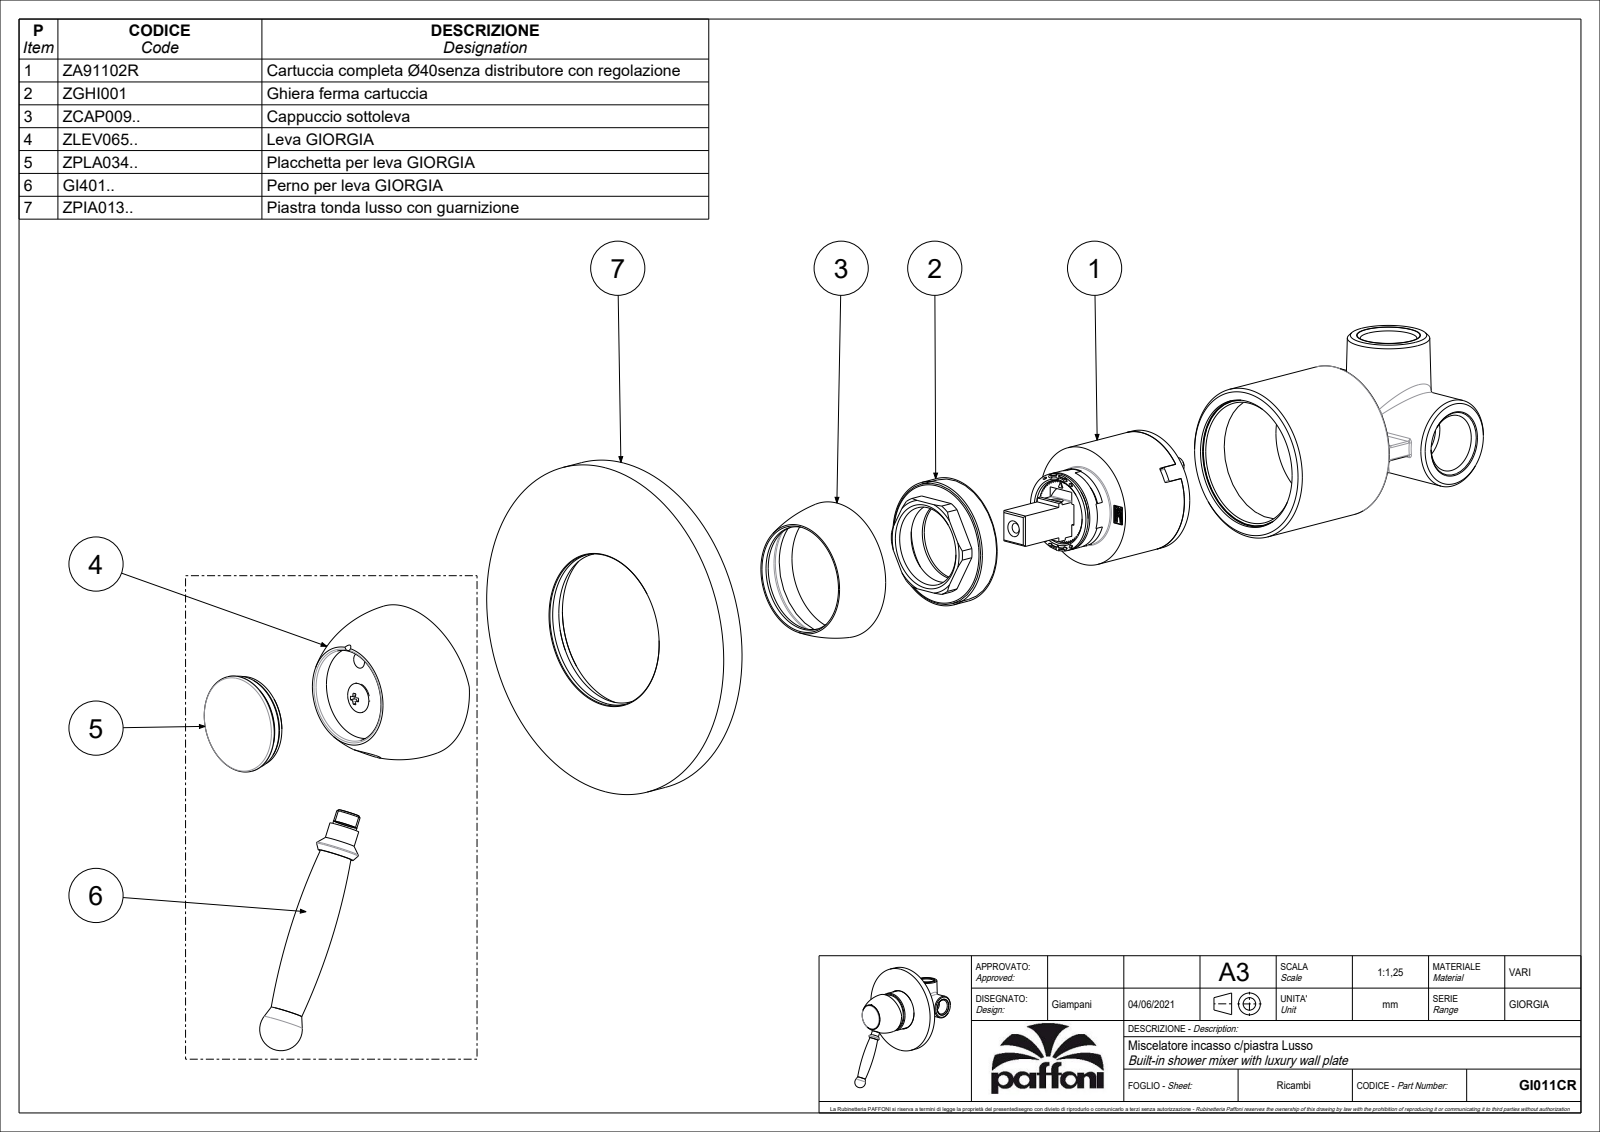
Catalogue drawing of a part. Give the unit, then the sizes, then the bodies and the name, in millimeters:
Units: millimetres
Overall size (bounding box): 146.52 × 110 × 90.37
Round holes (diameter × count): ⌀5 ×2, ⌀12 ×1, ⌀30.3 ×1, ⌀50.7 ×1, ⌀52.7 ×1, ⌀56.6 ×1, ⌀105 ×1
Round bosses / shafts (diameter × count): ⌀110 ×1, ⌀59.7 ×1, ⌀50 ×1, ⌀32 ×1, ⌀29.9 ×1, ⌀27 ×1, ⌀17.5 ×1, ⌀9.9 ×1
Partial cylindrical surfaces — rounded edges, fillets, slot ends (radius × count): R2 ×1, R3.5 ×1, R24.35 ×1
Main face-to-face distances: 7, 6.91, 43, 42.91, 36, 57.7, 57.61, 50.7, 14.7, 10
Hole centre spacings: 1.47, 1.6, 11, 11.13, 12.6
Volume: 125 851 mm³ · Surface area: 62 676 mm²
Bodies: 1 solid, 117 faces (35 planar, 40 cylindrical, 42 other)
Part name (STEP PRODUCT): GI011CR
STEP written by: CREO PARAMETRIC BY PTC INC, 2020044 (CONFIG_CONTROL_DESIGN)
